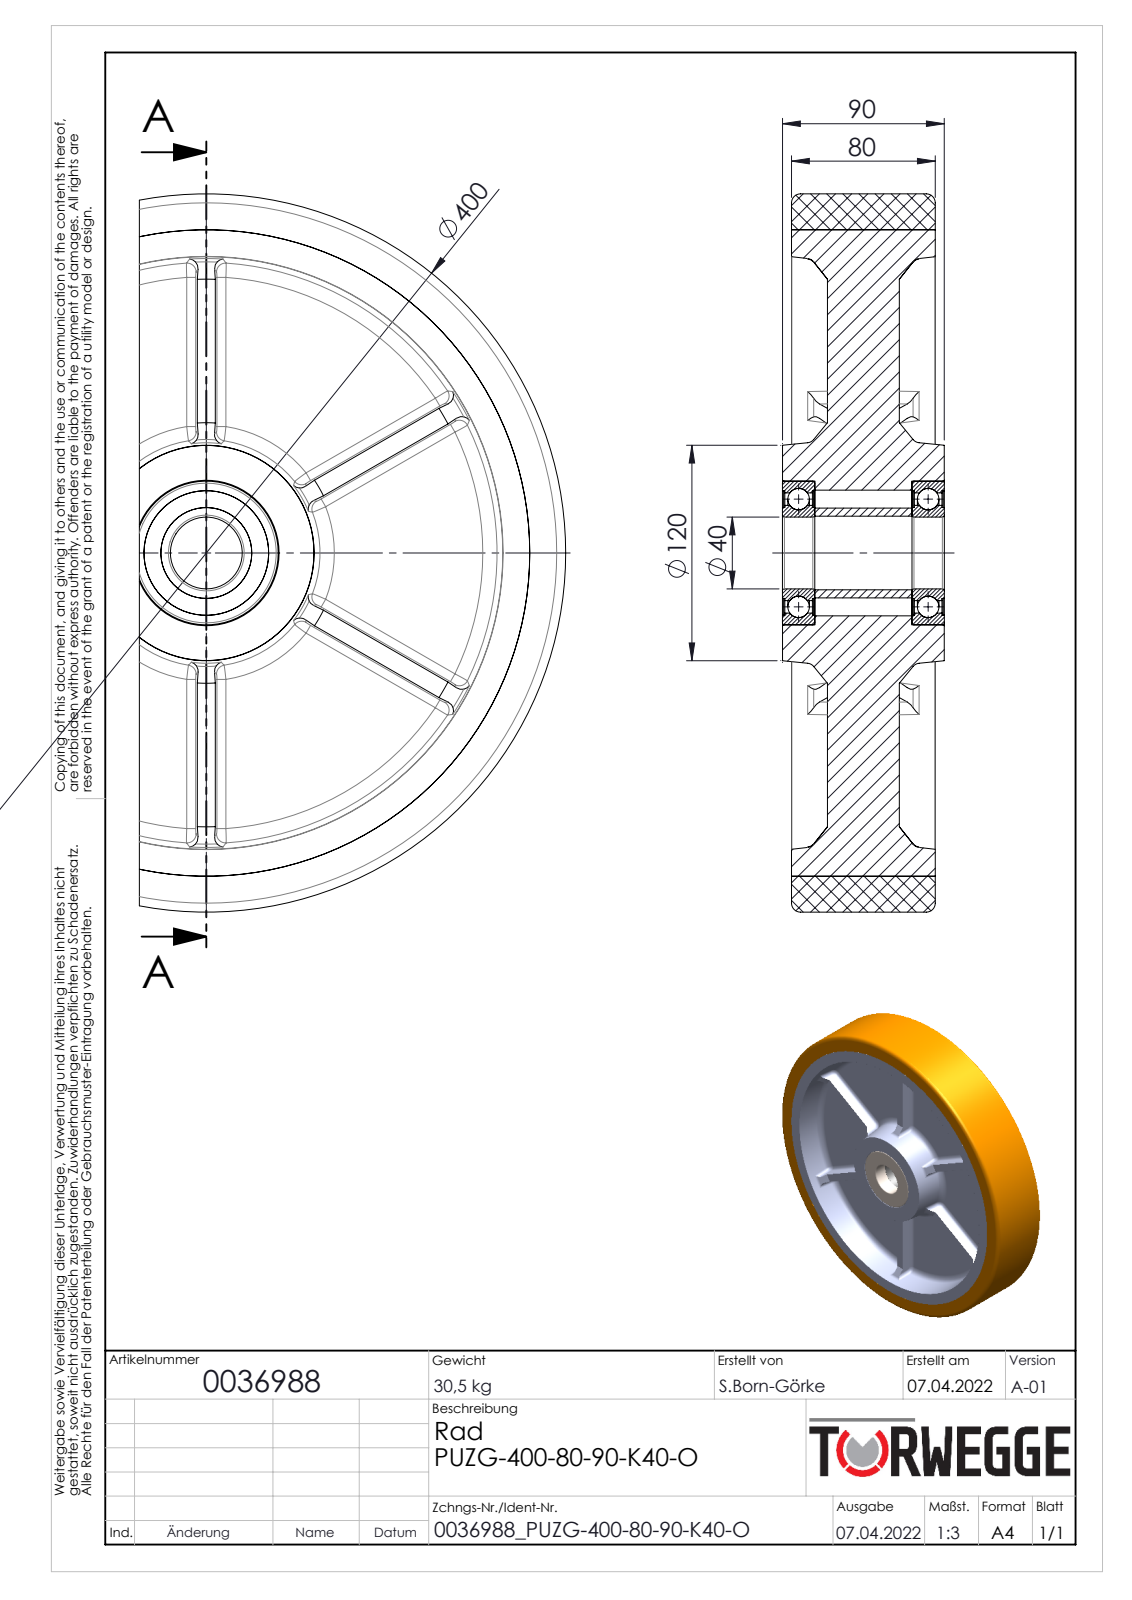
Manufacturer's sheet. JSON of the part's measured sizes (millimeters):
{"part_name": "0036988", "step_written_by": "SolidWorks 2020 (AUTOMOTIVE_DESIGN)", "units": "millimeters", "bodies": {"solids": 13, "faces": 410, "planar": 82, "cylindrical": 96, "other": 232}, "overall_size": [400, 400, 90.1], "volume_mm3": 5182000, "surface_area_mm2": 732760, "round_holes": [[40, 1], [41, 1], [50.6, 1], [66.96, 1], [69.4, 1], [70, 1], [80, 1], [360, 1]], "round_bosses_or_shafts": [[400, 1], [53.04, 1], [50, 1]], "partial_cylinders_radius": [[5, 16]], "face_to_face_distances": [35, 45, 10, 80, 25, 40, 5, 50, 85, 13.44]}
